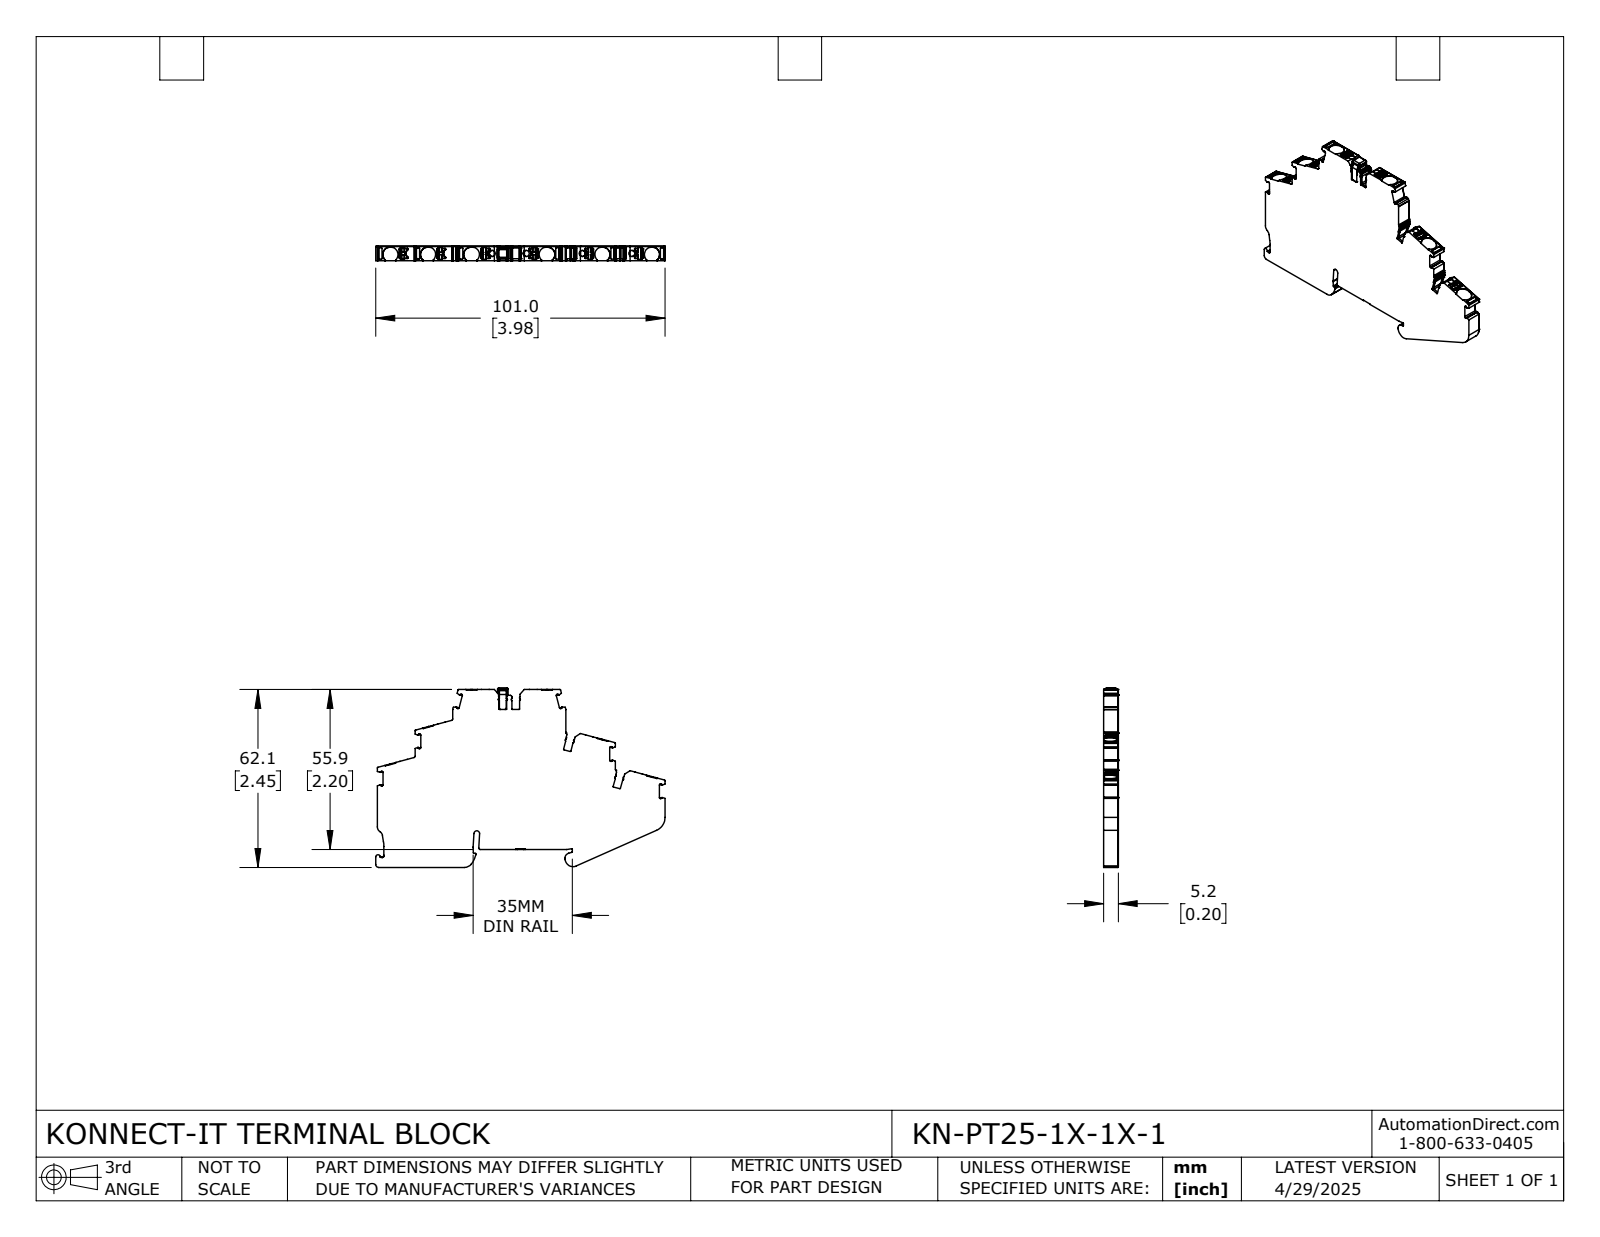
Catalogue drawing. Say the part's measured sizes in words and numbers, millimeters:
The part is named "KN-PT25-1X-1X-1". Its 3-D file was written by "SolidWorks 2024 (CONFIG_CONTROL_DESIGN)". It is 1 solid with 1314 faces: 638 planar, 565 cylindrical and 111 other. Overall it measures 101 by 62.7 by 5.2 millimeters. Its volume is 22 290 cubic millimeters and its surface area 10 910 square millimeters. Round holes: 4 of diameter 2.1. Partial cylindrical surfaces (rounded edges, fillets, slot ends): 132 of radius 0.2, 51 of radius 0.3, 49 of radius 0.1, 34 of radius 0.5, 24 of radius 0.2, 17 of radius 0.4, 14 of radius 0.6, 12 of radius 0.2. The main face-to-face distances are 5.2, 6.2, 2, 55.7, 61.9, 8.1, 17.3, 13.2, 55.9, 62.1. The hole center spacings are 11.8, 20.1.
